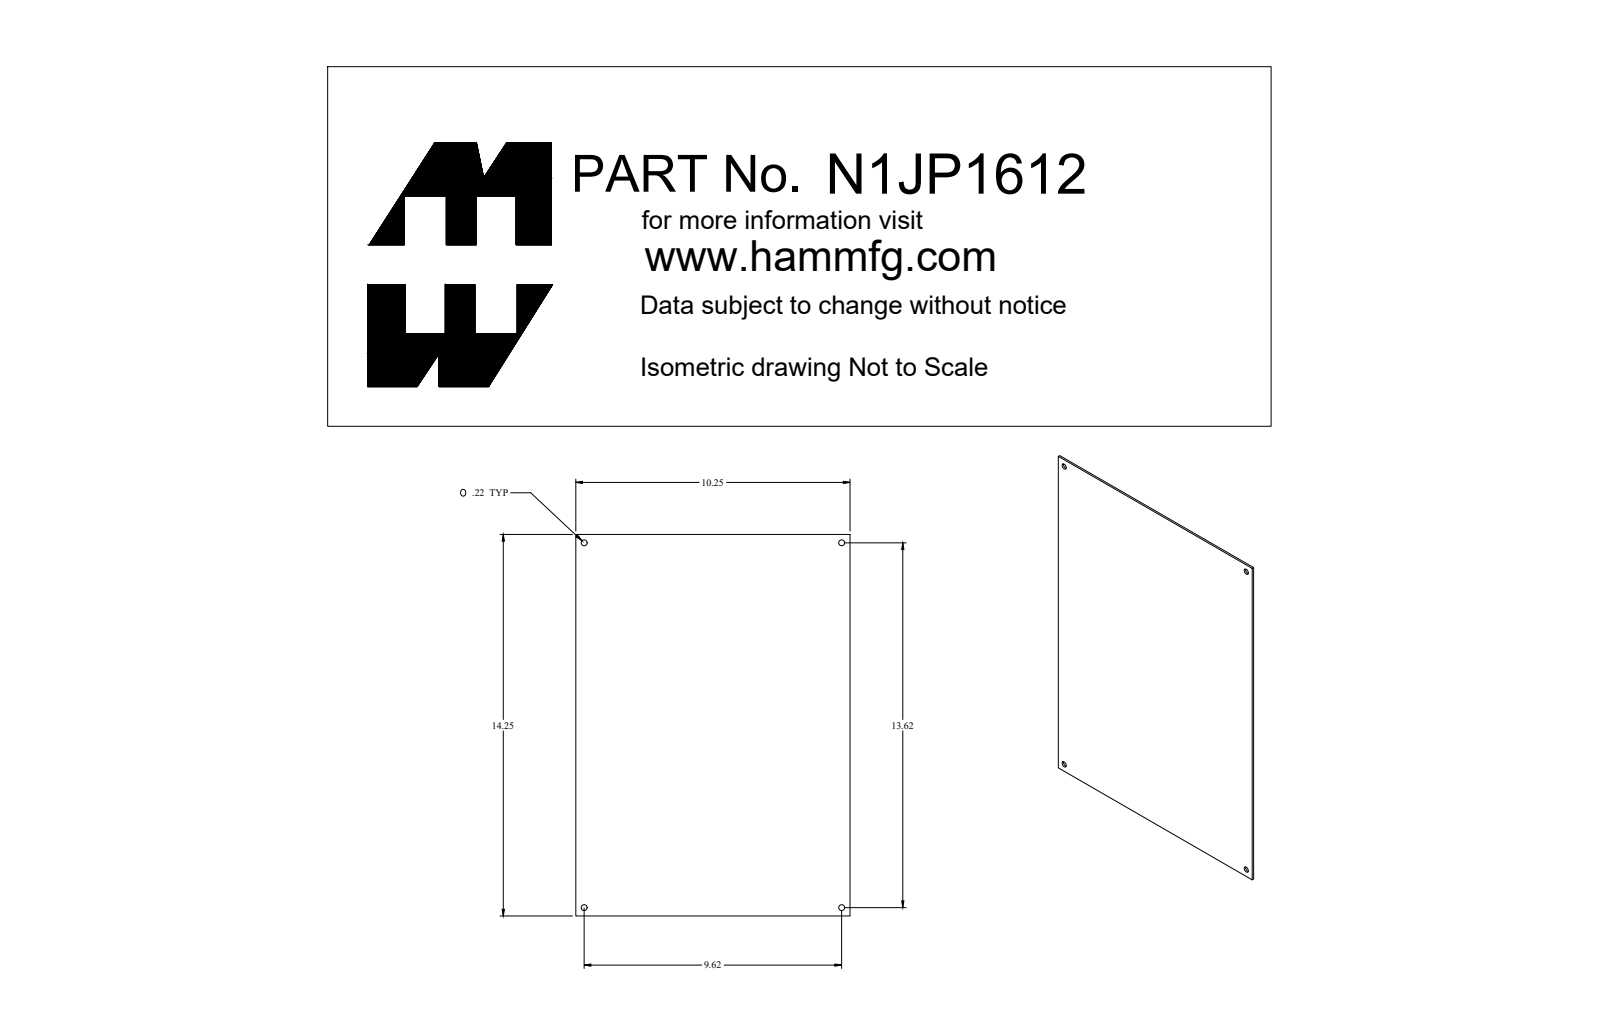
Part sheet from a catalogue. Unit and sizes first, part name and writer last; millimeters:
Units: millimetres
Overall size (bounding box): 362 × 260.4 × 1.8
Round holes (diameter × count): ⌀6.7 ×4
Partial cylindrical surfaces — rounded edges, fillets, slot ends (radius × count): R3.2 ×4
Main face-to-face distances: 1.8, 260.4, 362
Hole centre spacings: 244.5, 346.1, 423.7
Volume: 172 100 mm³ · Surface area: 190 600 mm²
Bodies: 1 solid, 18 faces (6 planar, 12 cylindrical, 0 other)
Part name (STEP PRODUCT): N1JP1612
STEP written by: SolidWorks 2018 (AUTOMOTIVE_DESIGN)
